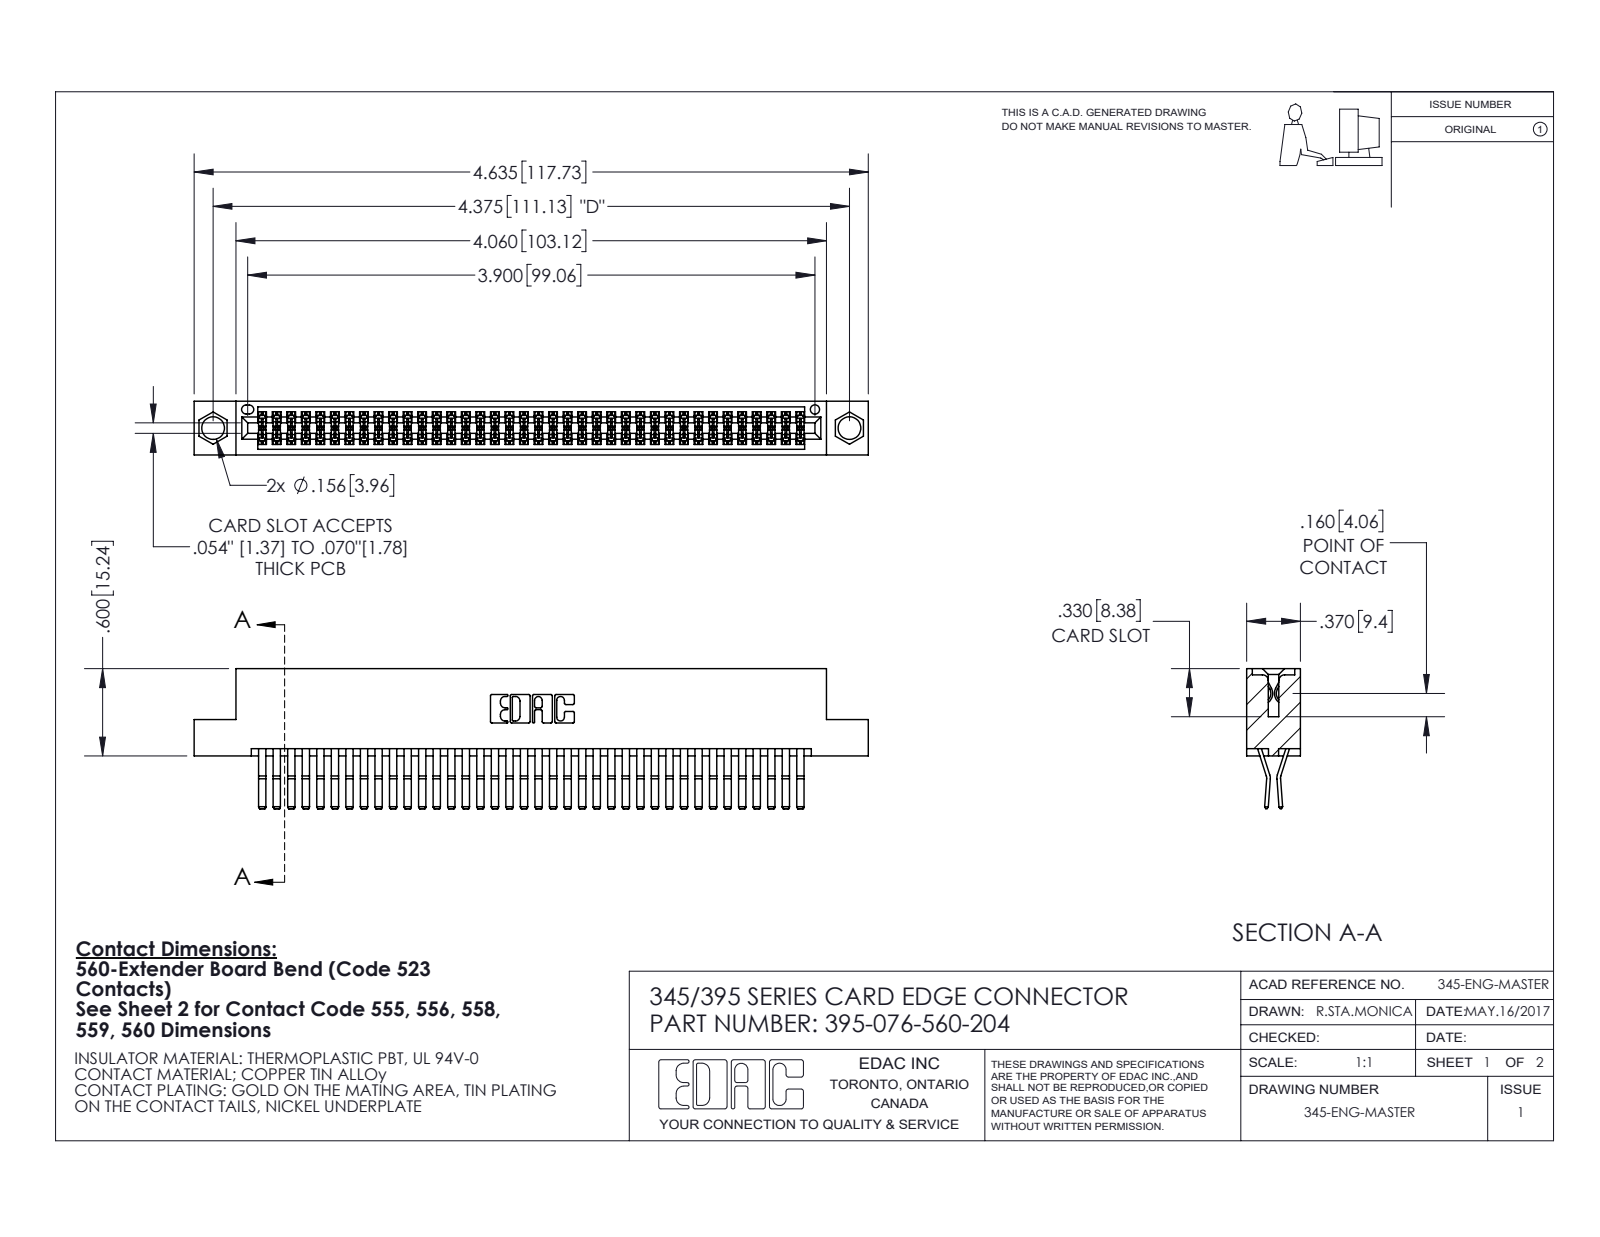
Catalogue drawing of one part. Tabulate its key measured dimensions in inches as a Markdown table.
| quantity | value |
| --- | --- |
| part name | 345-292-001_560 Tail; 345 Part_Flush Mounting Lugs - 0.156 Dia-TI; 395-076-560-204 |
| STEP written by | SolidWorks 2020 (CONFIG_CONTROL_DESIGN) |
| units | inches |
| bodies | 77 solids, 4092 faces (2602 planar, 1490 cylindrical, 0 other) |
| overall size | 4.635 × 0.962 × 0.37 |
| volume | 0.72 in³ |
| surface area | 28.65 in² |
| round holes (diameter × count) | 0.156 × 2, 0.064 × 1 |
| partial cylindrical surfaces (radius × count) | 0.006 × 114, 0.01 × 22, 0.007 × 6, 0.031 × 6, 0.026 × 3, 0.01 × 2, 0.014 × 2, 0.019 × 2 |
| main face-to-face distances | 0.025, 0.298, 0.072, 0.2, 0.37, 0.098, 0.272, 0.225, 0.175, 0.149 |
| hole center spacings | 0.27, 4.139, 4.375 |
